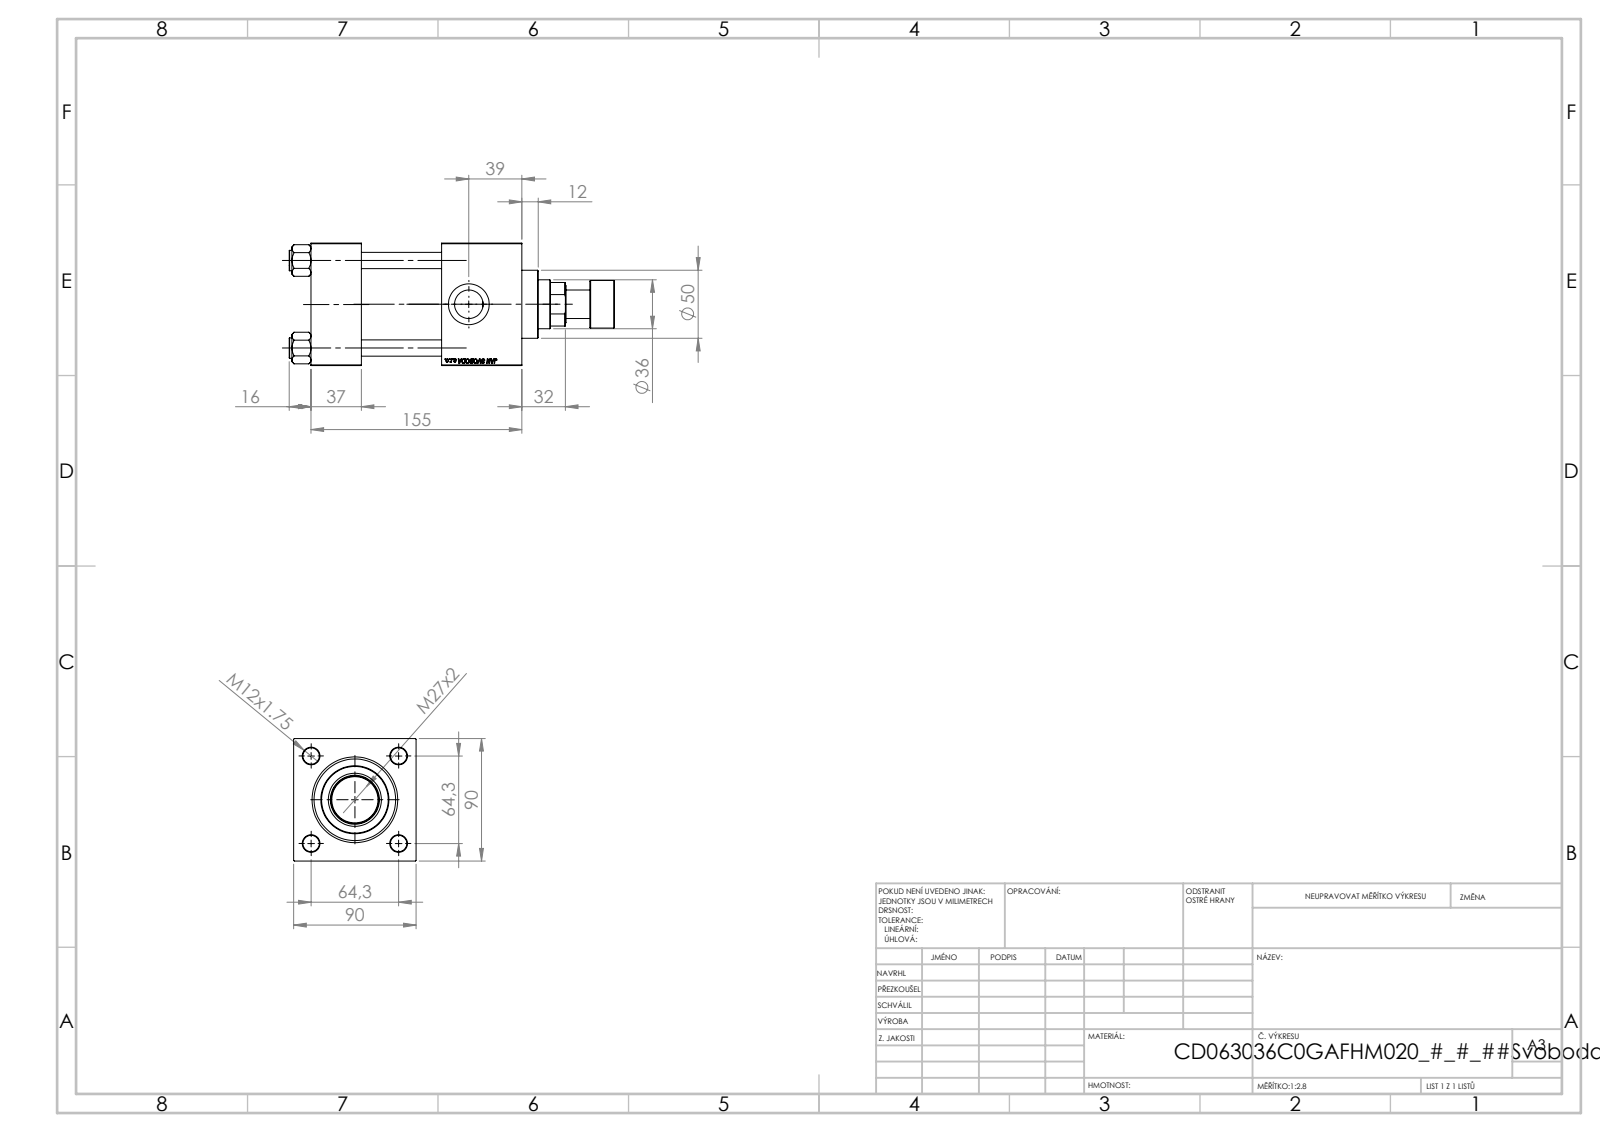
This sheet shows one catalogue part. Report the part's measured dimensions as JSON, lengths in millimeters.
{"part_name": "V215CD_VCP_C; V215CD_VC_C; V215CD_Body_C; NUT_M5_V215CD_C (+2 more)", "step_written_by": "SolidWorks 2019 (CONFIG_CONTROL_DESIGN)", "units": "millimeters", "bodies": {"solids": 12, "faces": 1163, "planar": 530, "cylindrical": 91, "other": 542}, "overall_size": [239, 90, 90], "volume_mm3": 991498, "surface_area_mm2": 189805, "round_holes": [[12, 4], [7, 2], [20.96, 2], [30, 2], [25.5, 1], [36, 1], [39, 1], [50, 1], [60, 1], [63, 1]], "round_bosses_or_shafts": [[15, 4], [69, 1], [35, 1], [21, 1]], "face_to_face_distances": [90, 59, 37, 96, 155, 118, 20, 126.3, 89.3, 30.3], "hole_center_spacings": [45.47, 64.3, 90.93]}
